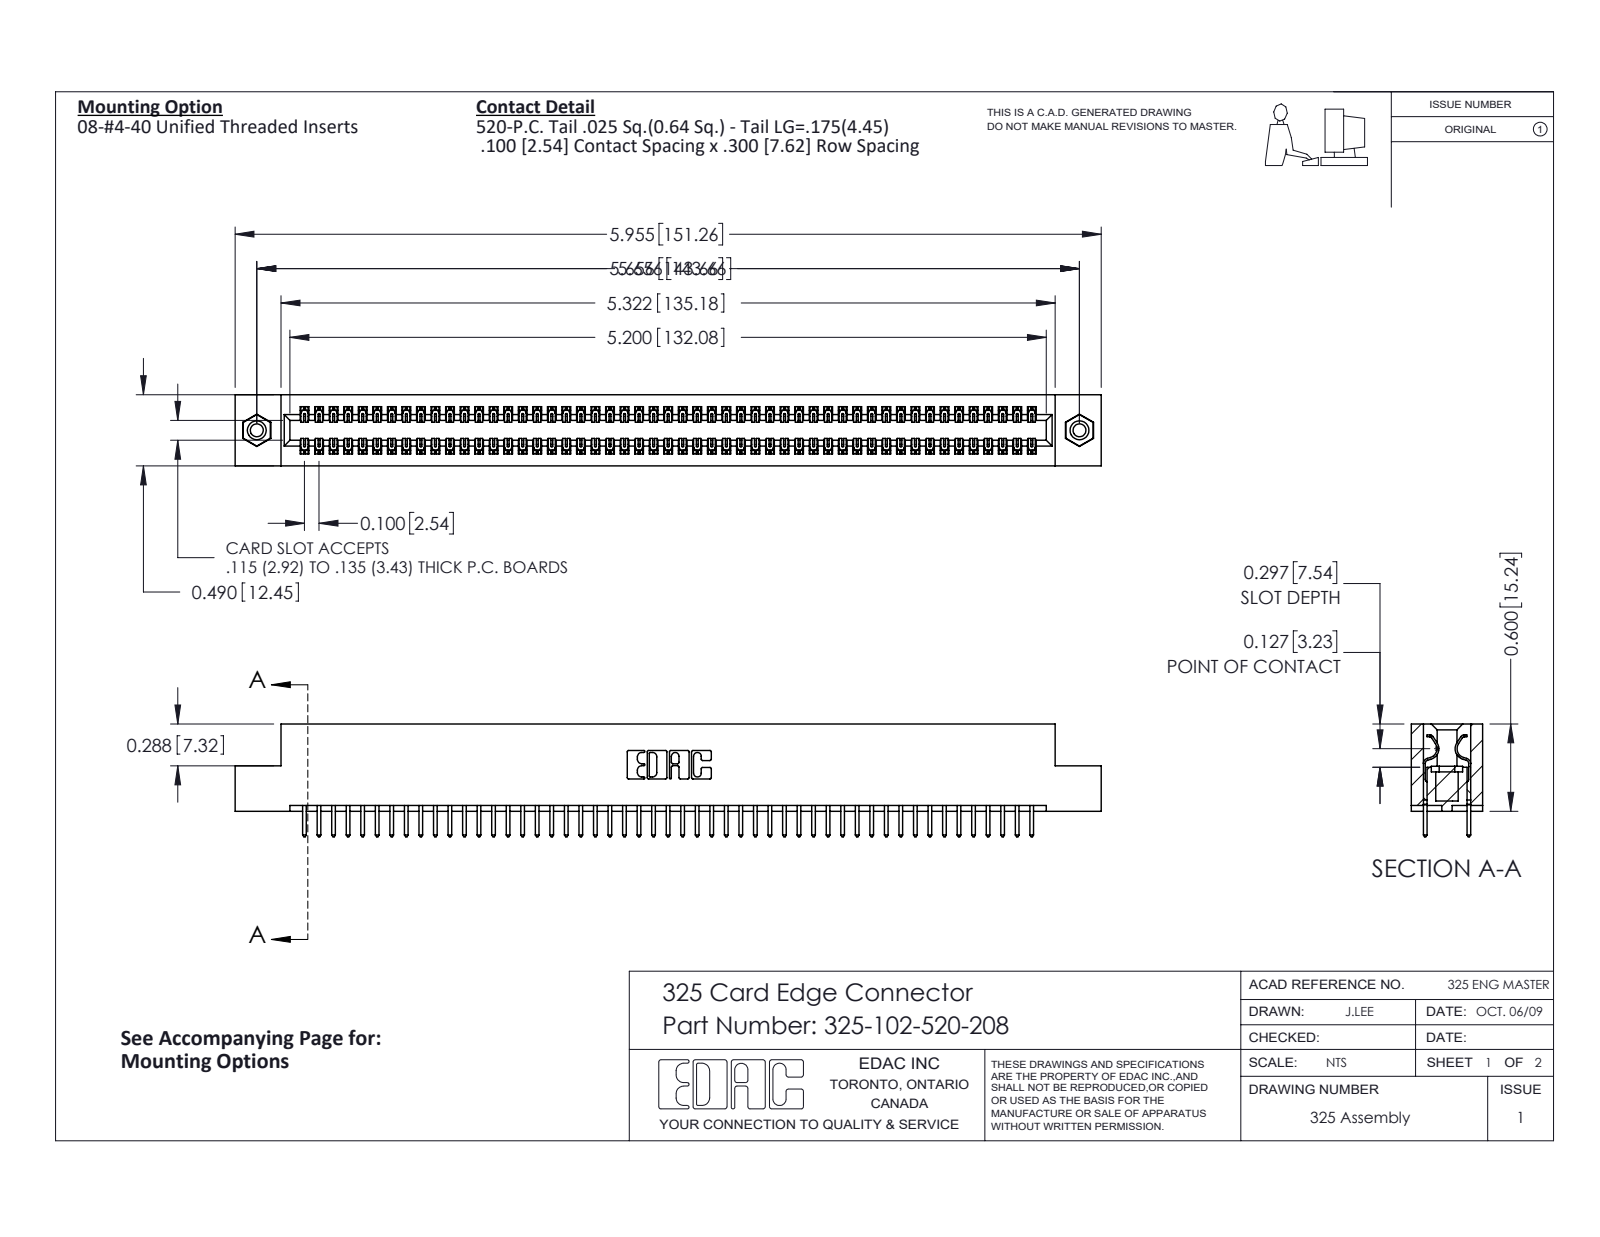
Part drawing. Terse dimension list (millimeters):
name: 325-102-520-208; 325-292-001_325-293-120; 345-250-001_345-250-003-102; 325 Part_TI
written by: SolidWorks 2016 (CONFIG_CONTROL_DESIGN)
unit: mm
bodies: 105 solids, 5478 faces (3774 planar, 1688 cylindrical, 16 other)
size: 151.3 × 19.7 × 12.4
volume: 19 580 mm³; area: 23 730 mm²
holes: 2× ⌀2.3, 2× ⌀3.2, 2× ⌀4.1
bosses: 2× ⌀3.9
rounds: 153× R0.2, 102× R0.3, 22× R0.3, 6× R0.2, 6× R0.8, 3× R0.7, 2× R0.4, 2× R0.6
face distances: 2.1, 10.3, 7.6, 12.4, 2.7, 9.7, 0.6, 8.3, 7, 14.2
hole spacings: 143.7
